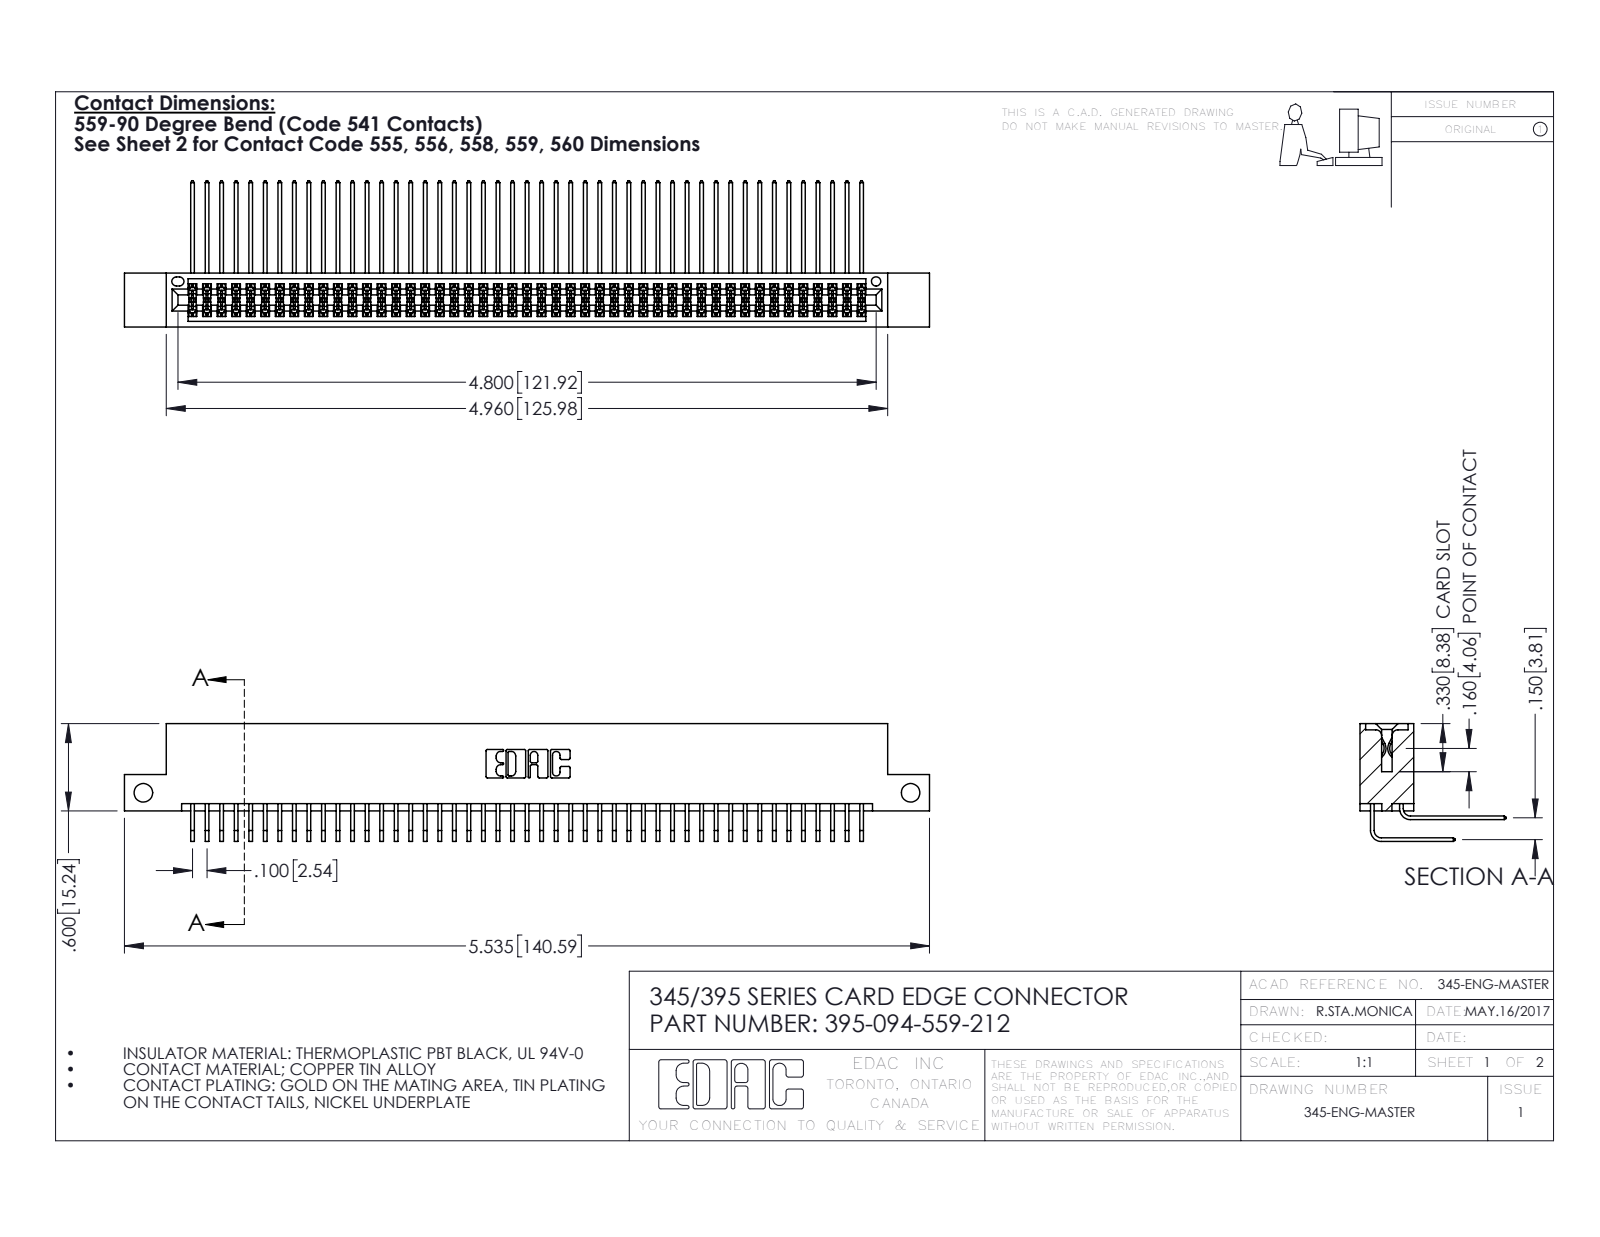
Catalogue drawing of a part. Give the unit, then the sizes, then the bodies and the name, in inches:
Units: inches
Overall size (bounding box): 5.535 × 1.005 × 0.809
Round holes (diameter × count): ⌀0.128 ×2, ⌀0.064 ×1
Partial cylindrical surfaces — rounded edges, fillets, slot ends (radius × count): R0.006 ×141, R0.01 ×22, R0.007 ×6, R0.031 ×6, R0.026 ×3, R0.014 ×2, R0.019 ×2, R0.022 ×2
Main face-to-face distances: 0.072, 0.298, 0.2, 0.37, 0.098, 0.272, 0.025, 0.225, 0.175, 0.15
Hole centre spacings: 5.275
Volume: 0.864 in³ · Surface area: 36.33 in²
Bodies: 95 solids, 5014 faces (3370 planar, 1644 cylindrical, 0 other)
Part name (STEP PRODUCT): 345 Part_Flush Mounting Lugs - Side Mount; 345-292-001_558 559 Tail - 1; 345-292-001_559 Tail - 2; 395-094-559-212
STEP written by: SolidWorks 2016 (CONFIG_CONTROL_DESIGN)
